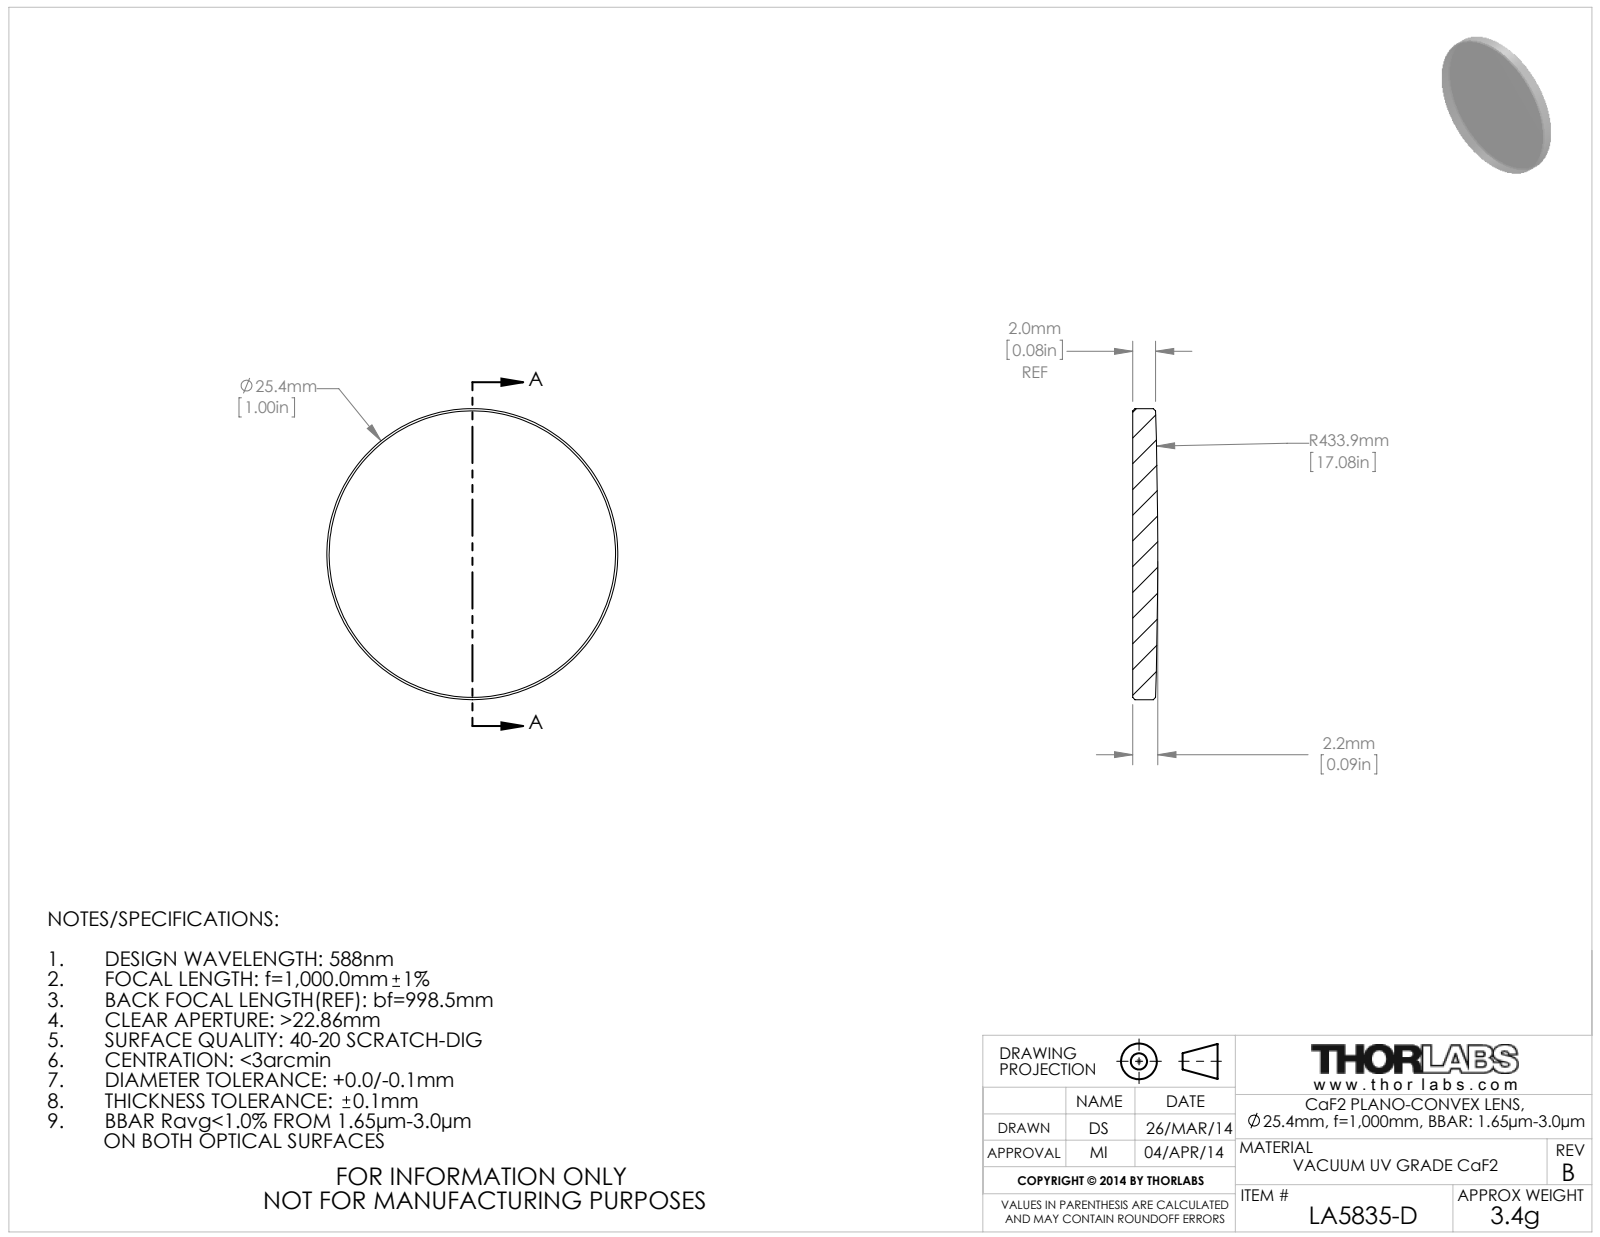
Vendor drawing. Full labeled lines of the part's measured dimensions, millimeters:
Part name (STEP PRODUCT): 22968-E0W
STEP written by: SolidWorks 2011 (AUTOMOTIVE_DESIGN)
Units: millimetres
Bodies: 0 solids, 5 faces (1 planar, 2 cylindrical, 2 other)
Overall size (bounding box): 25.4 × 25.4 × 2.18
Round bosses / shafts (diameter × count): ⌀25.4 ×1
